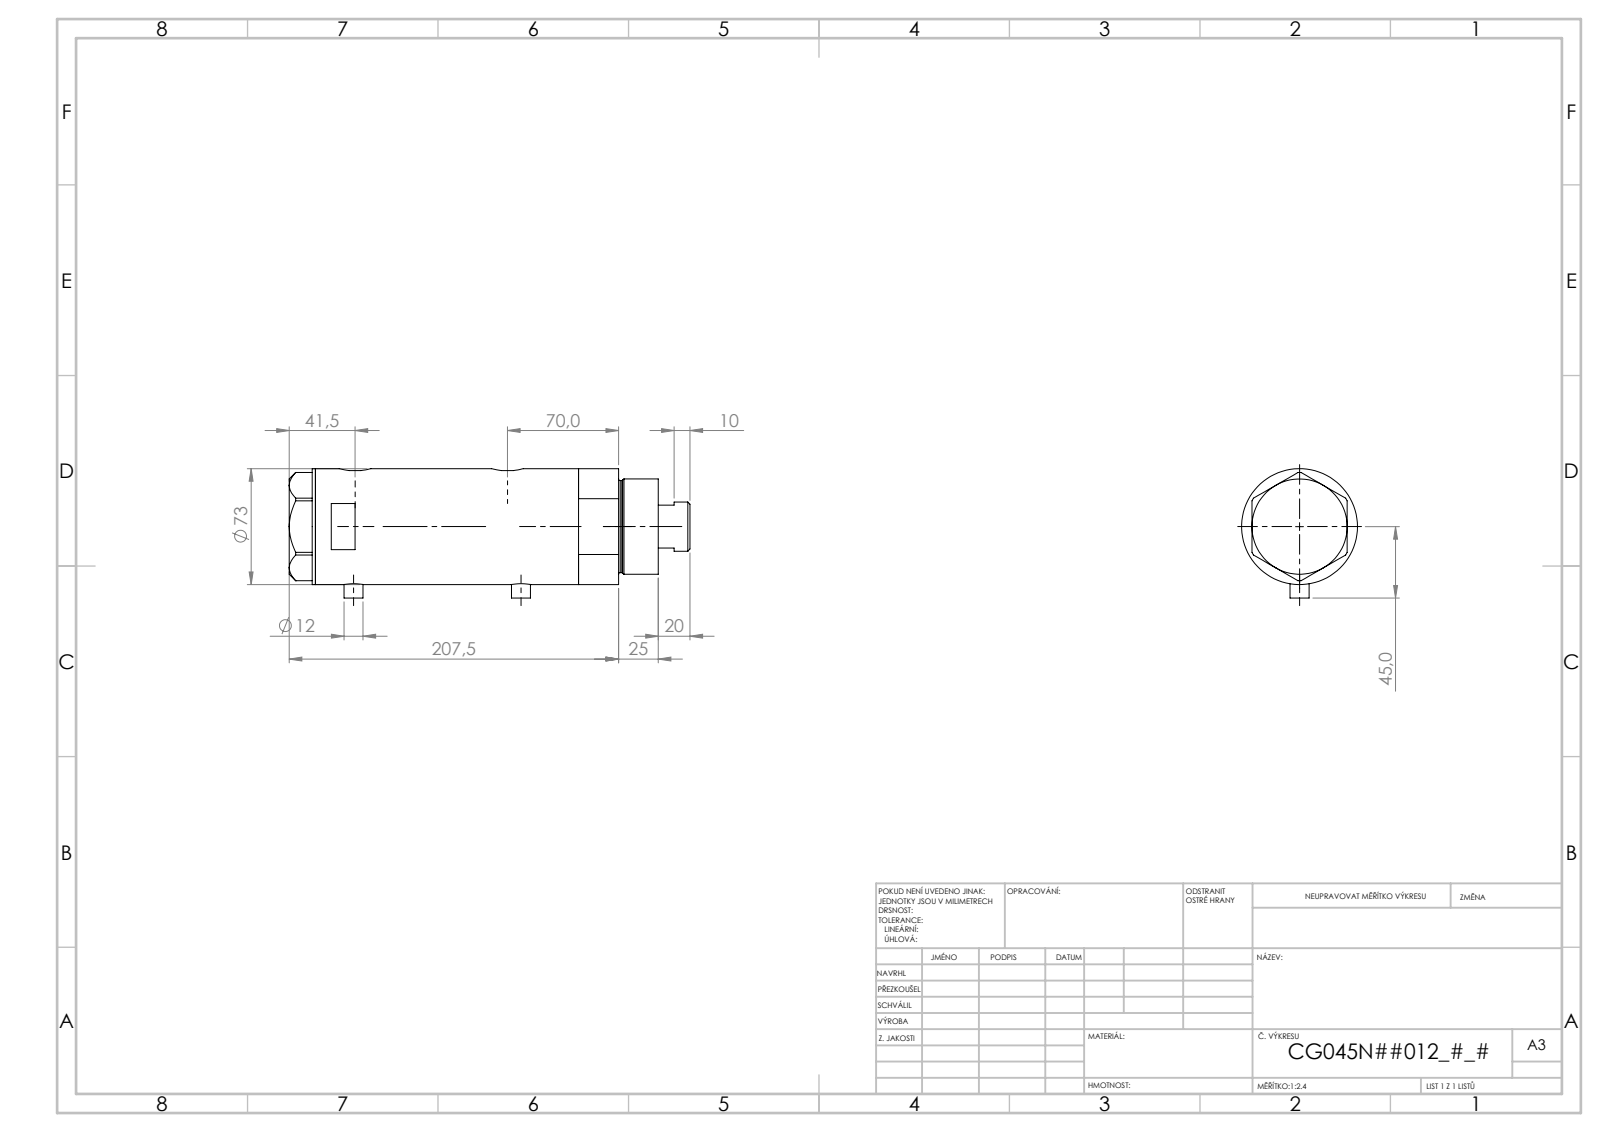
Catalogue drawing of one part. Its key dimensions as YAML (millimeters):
part_name: "V270CG_MIDDLE; V270CG_BACK; V270CG_FRONT; V270CG_VC"
step_written_by: "SolidWorks 2019 (CONFIG_CONTROL_DESIGN)"
units: millimeters
bodies: {solids: 4, faces: 125, planar: 50, cylindrical: 55, other: 20}
overall_size: [203.52, 74.1, 73]
volume: 707546
surface_area: 125595
round_holes:
  - {diameter: 5, count: 2}
  - {diameter: 12.5, count: 2}
  - {diameter: 13.16, count: 2}
  - {diameter: 10.5, count: 1}
  - {diameter: 32, count: 1}
  - {diameter: 33.5, count: 1}
  - {diameter: 45, count: 1}
  - {diameter: 48, count: 1}
  - {diameter: 64, count: 1}
round_bosses_or_shafts:
  - {diameter: 12, count: 2}
  - {diameter: 73, count: 1}
  - {diameter: 60, count: 1}
  - {diameter: 58, count: 1}
  - {diameter: 31, count: 1}
partial_cylinders:
  - {radius: 10, count: 2}
face_to_face_distances: [79.16, 26, 53.16, 16.49, 42.49, 95.65, 167.03, 183.52, 141.03, 87.87]
hole_center_spacings: [63.65, 0.99, 1, 8.5, 8.51, 54.15, 55.14, 55.15]
